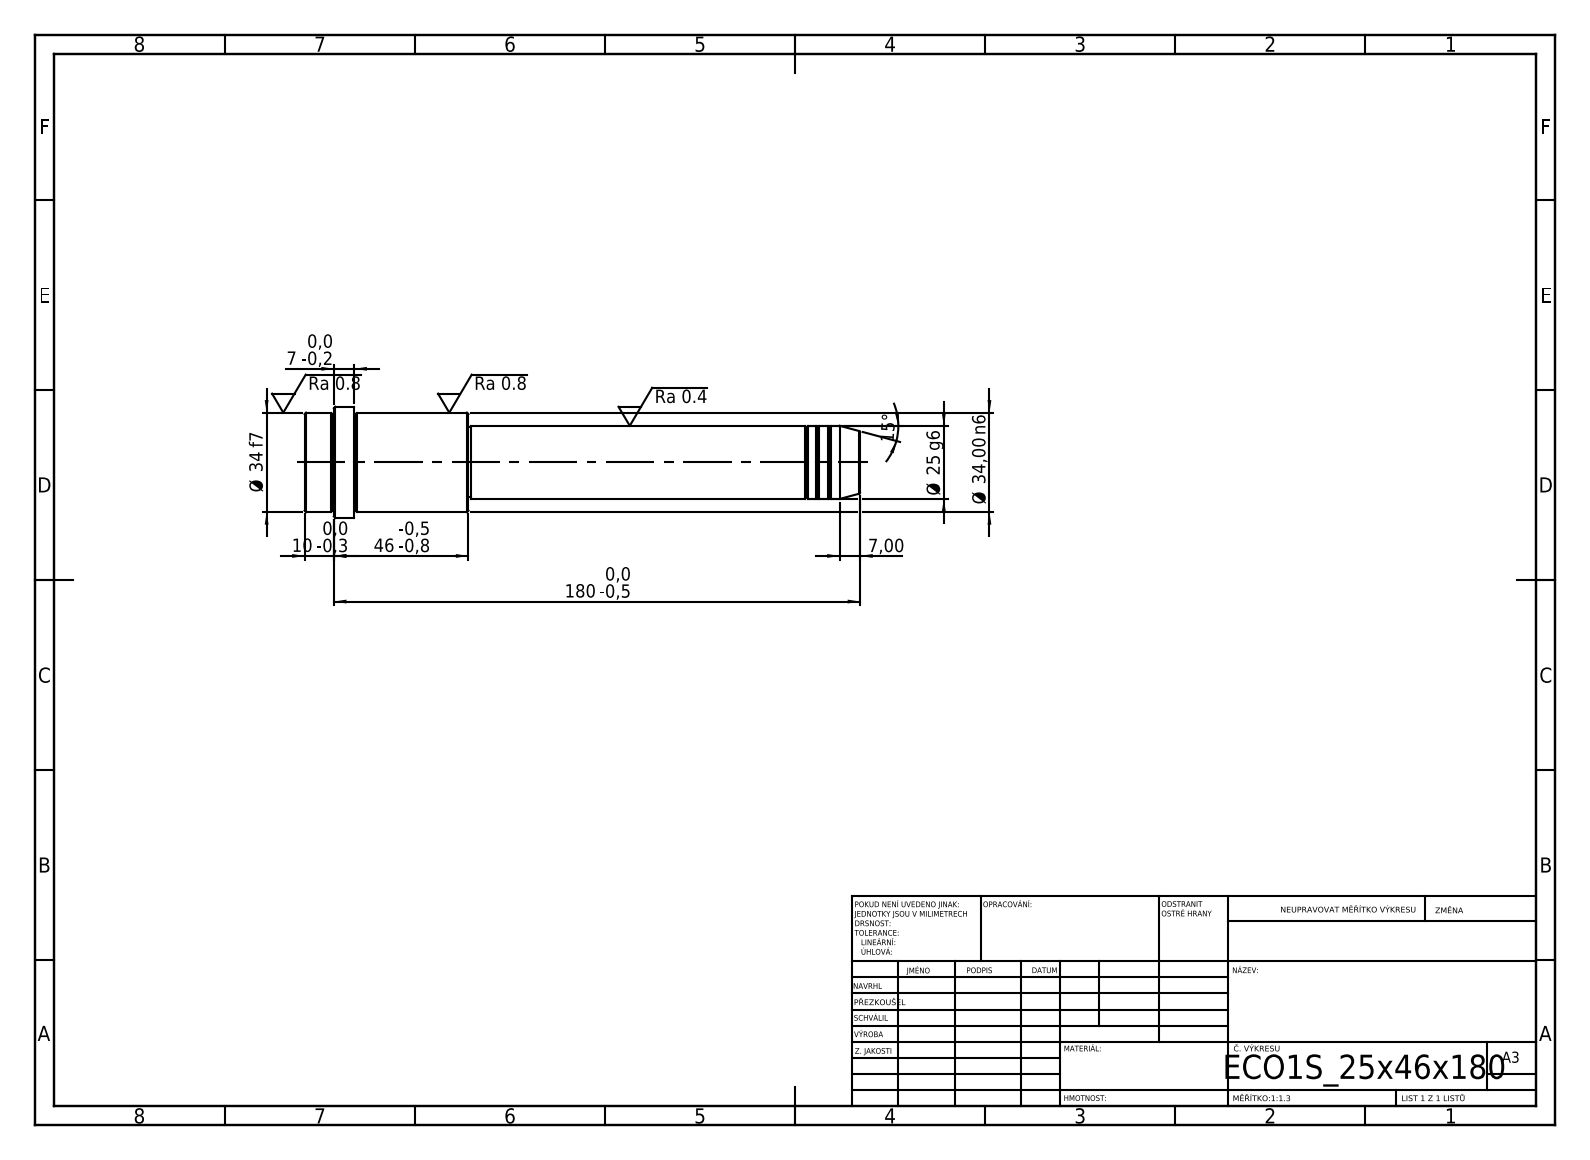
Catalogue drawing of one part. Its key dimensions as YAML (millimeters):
step_written_by: "SolidWorks 2019 (CONFIG_CONTROL_DESIGN)"
units: millimeters
bodies: {solids: 1, faces: 52, planar: 6, cylindrical: 16, other: 30}
overall_size: [190, 38, 38]
volume: 117459
surface_area: 18911
round_bosses_or_shafts:
  - {diameter: 38, count: 1}
  - {diameter: 34, count: 1}
  - {diameter: 25, count: 1}
  - {diameter: 24, count: 1}
face_to_face_distances: [56, 134, 190, 173, 39, 17, 180, 46, 7, 10]
